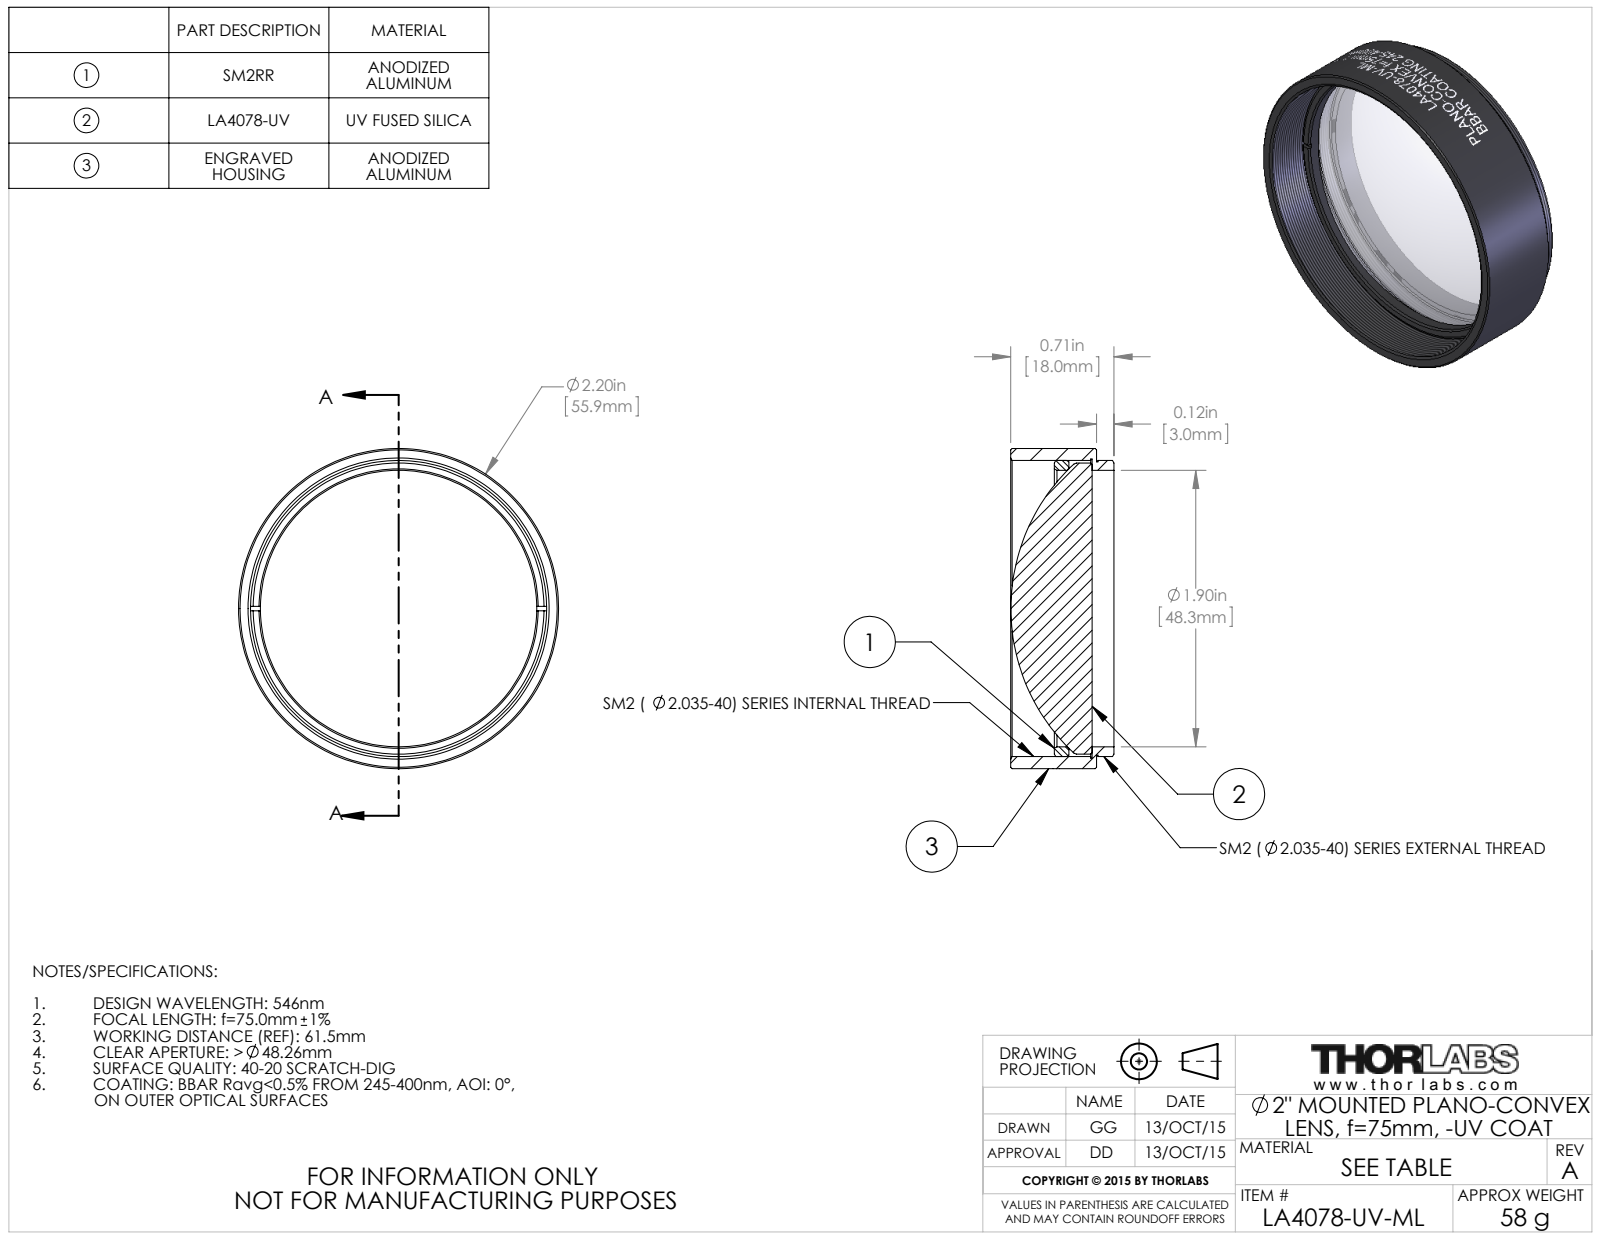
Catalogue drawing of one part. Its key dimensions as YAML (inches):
part_name: "TTN039138-E0W"
step_written_by: "SolidWorks 2014 (CONFIG_CONTROL_DESIGN)"
units: inches
bodies: {solids: 3, faces: 147, planar: 16, cylindrical: 107, other: 24}
overall_size: [2.2, 2.2, 0.71]
volume: 1.53
surface_area: 20.82
round_holes:
  - {diameter: 1.9, count: 1}
  - {diameter: 2.055, count: 1}
round_bosses_or_shafts:
  - {diameter: 2.2, count: 1}
  - {diameter: 2.035, count: 1}
  - {diameter: 2.015, count: 1}
  - {diameter: 2, count: 1}
face_to_face_distances: [0.03, 0.59, 0.56, 0.12, 0.15, 0.71, 0.31, 0.19, 0.16, 0.4]
